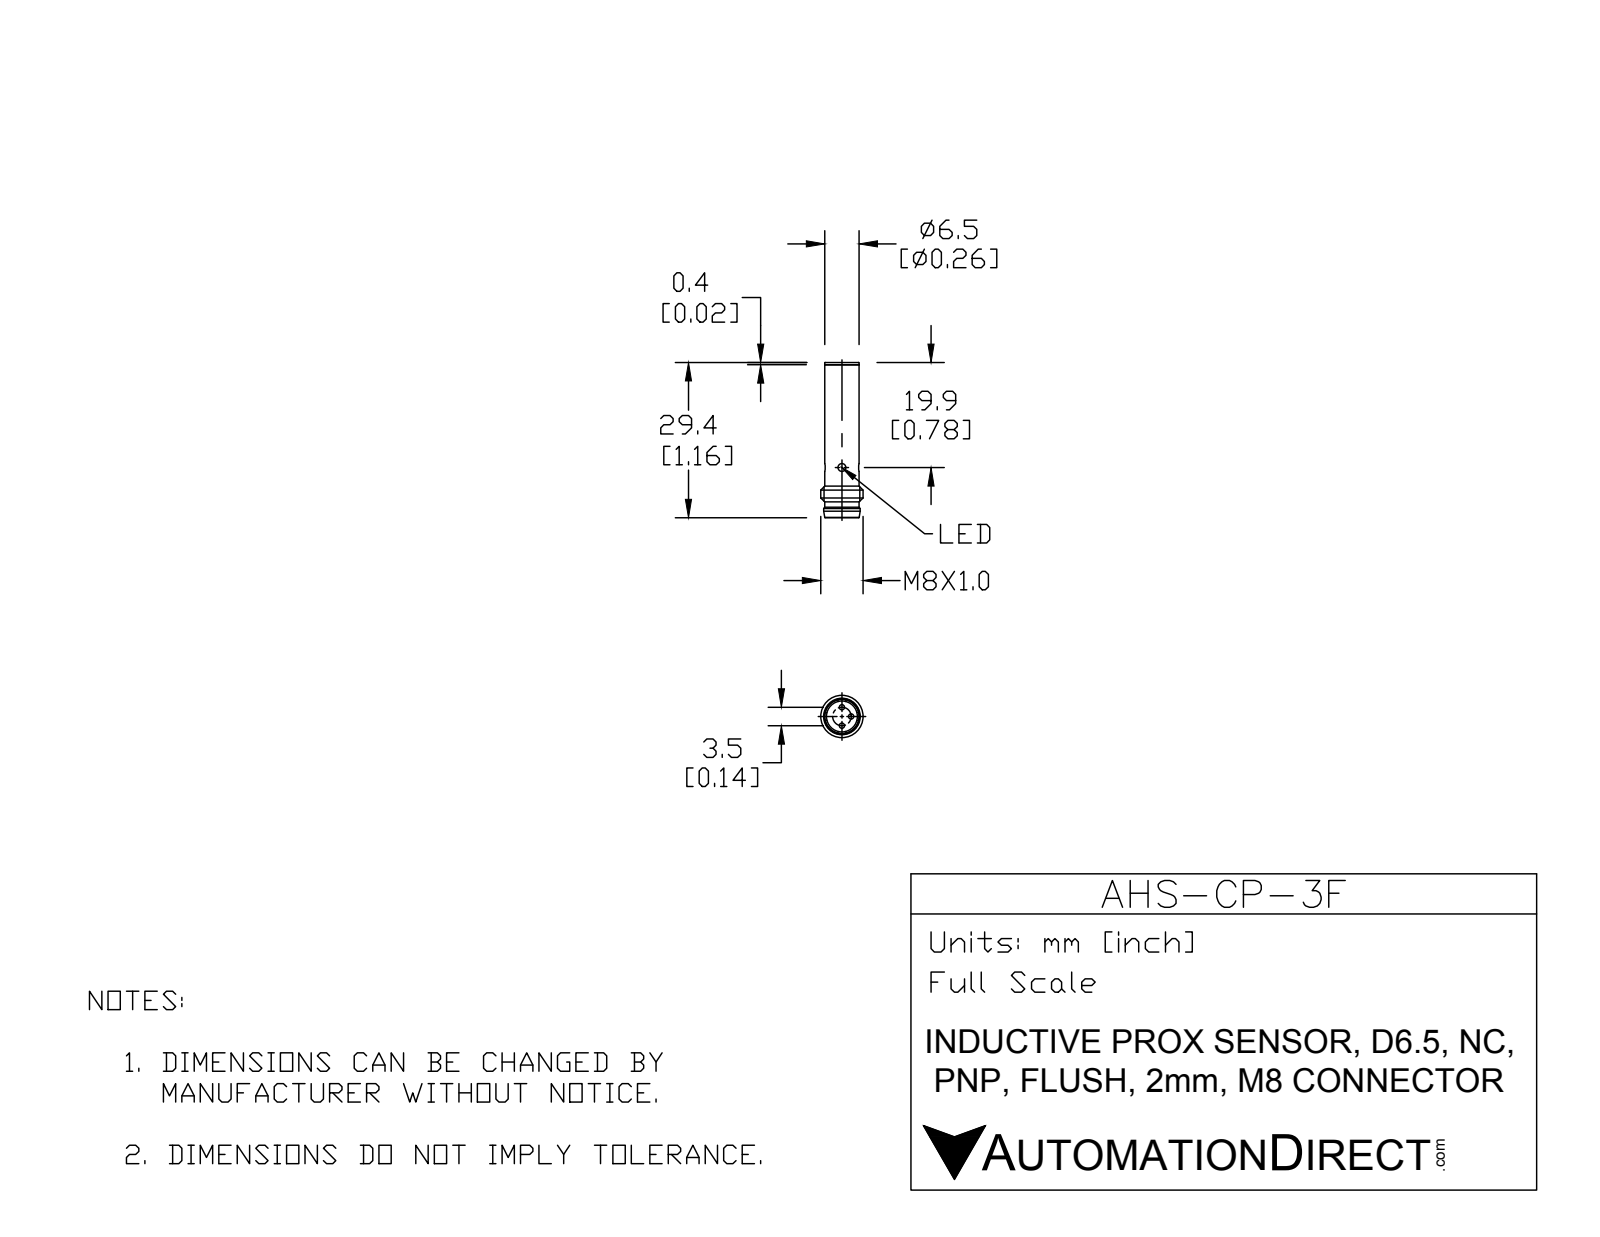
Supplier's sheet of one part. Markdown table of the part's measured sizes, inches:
| quantity | value |
| --- | --- |
| part name | AHS-CP-3F |
| STEP written by | SolidWorks 2015 (CONFIG_CONTROL_DESIGN) |
| units | inches |
| bodies | 4 solids, 56 faces (12 planar, 26 cylindrical, 18 other) |
| overall size | 1.157 × 0.315 × 0.315 |
| volume | 0.054 in³ |
| surface area | 1.31 in² |
| round holes (diameter × count) | 0.059 × 2, 0.23 × 1 |
| round bosses / shafts (diameter × count) | 0.039 × 3, 0.315 × 1, 0.272 × 1, 0.256 × 1 |
| main face-to-face distances | 0.961, 0.118, 1.079, 0.217, 0.079, 0.197, 1.157, 1.142, 1.063, 0.945 |
